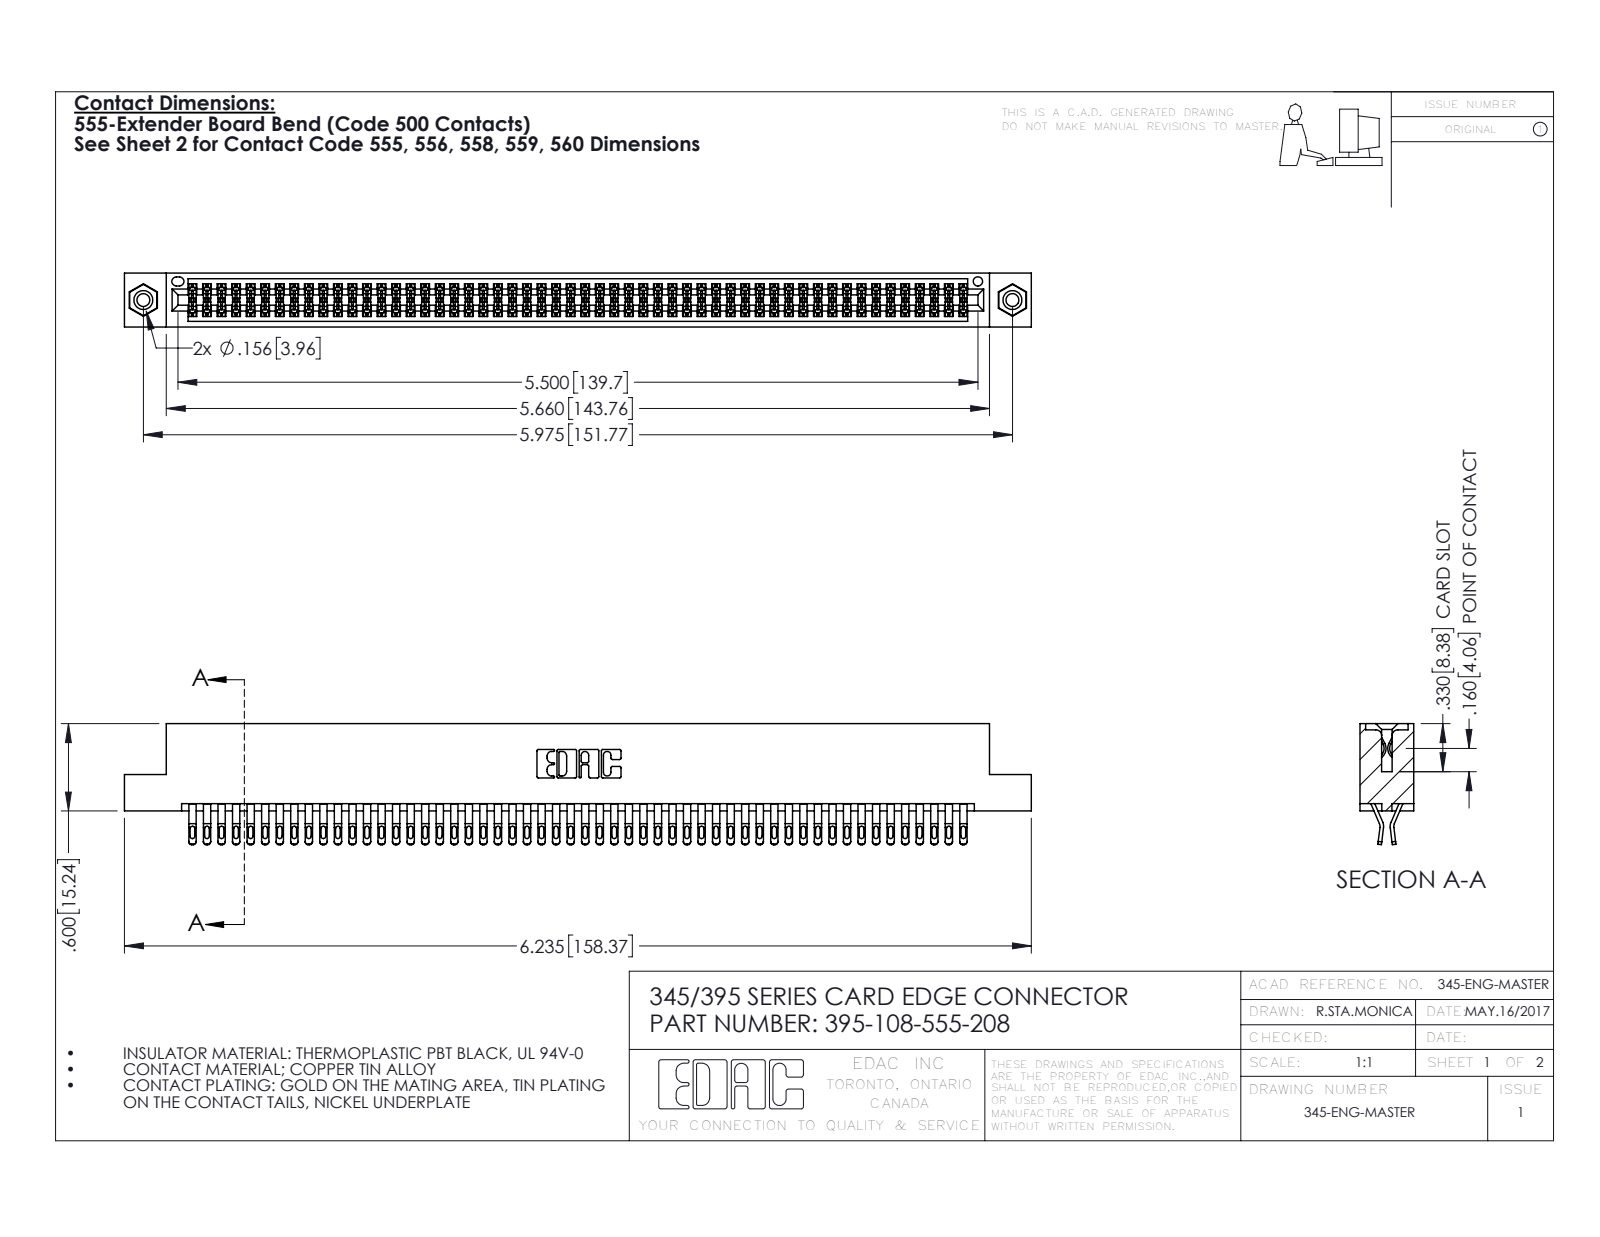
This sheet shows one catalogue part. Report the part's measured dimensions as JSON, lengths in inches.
{"part_name": "345 Part_Flush Mounting Lugs - 0.156 Dia-TI; 345-250-001_345-250-003-102; 395-108-555-208; 345-292-001_555 Tail", "step_written_by": "SolidWorks 2016 (CONFIG_CONTROL_DESIGN)", "units": "inches", "bodies": {"solids": 111, "faces": 6234, "planar": 3460, "cylindrical": 2758, "other": 16}, "overall_size": [6.235, 0.832, 0.37], "volume_in3": 0.964, "surface_area_in2": 38.28, "round_holes": [[0.089, 2], [0.125, 2], [0.156, 2], [0.064, 1]], "round_bosses_or_shafts": [[0.155, 2]], "partial_cylinders_radius": [[0.016, 270], [0.02, 216], [0.006, 162], [0.01, 22], [0.007, 6], [0.031, 6], [0.026, 3], [0.01, 2]], "face_to_face_distances": [0.072, 0.298, 0.025, 0.37, 0.2, 0.098, 0.272, 0.225, 0.175, 0.149], "hole_center_spacings": [0.27, 5.739, 5.975]}
